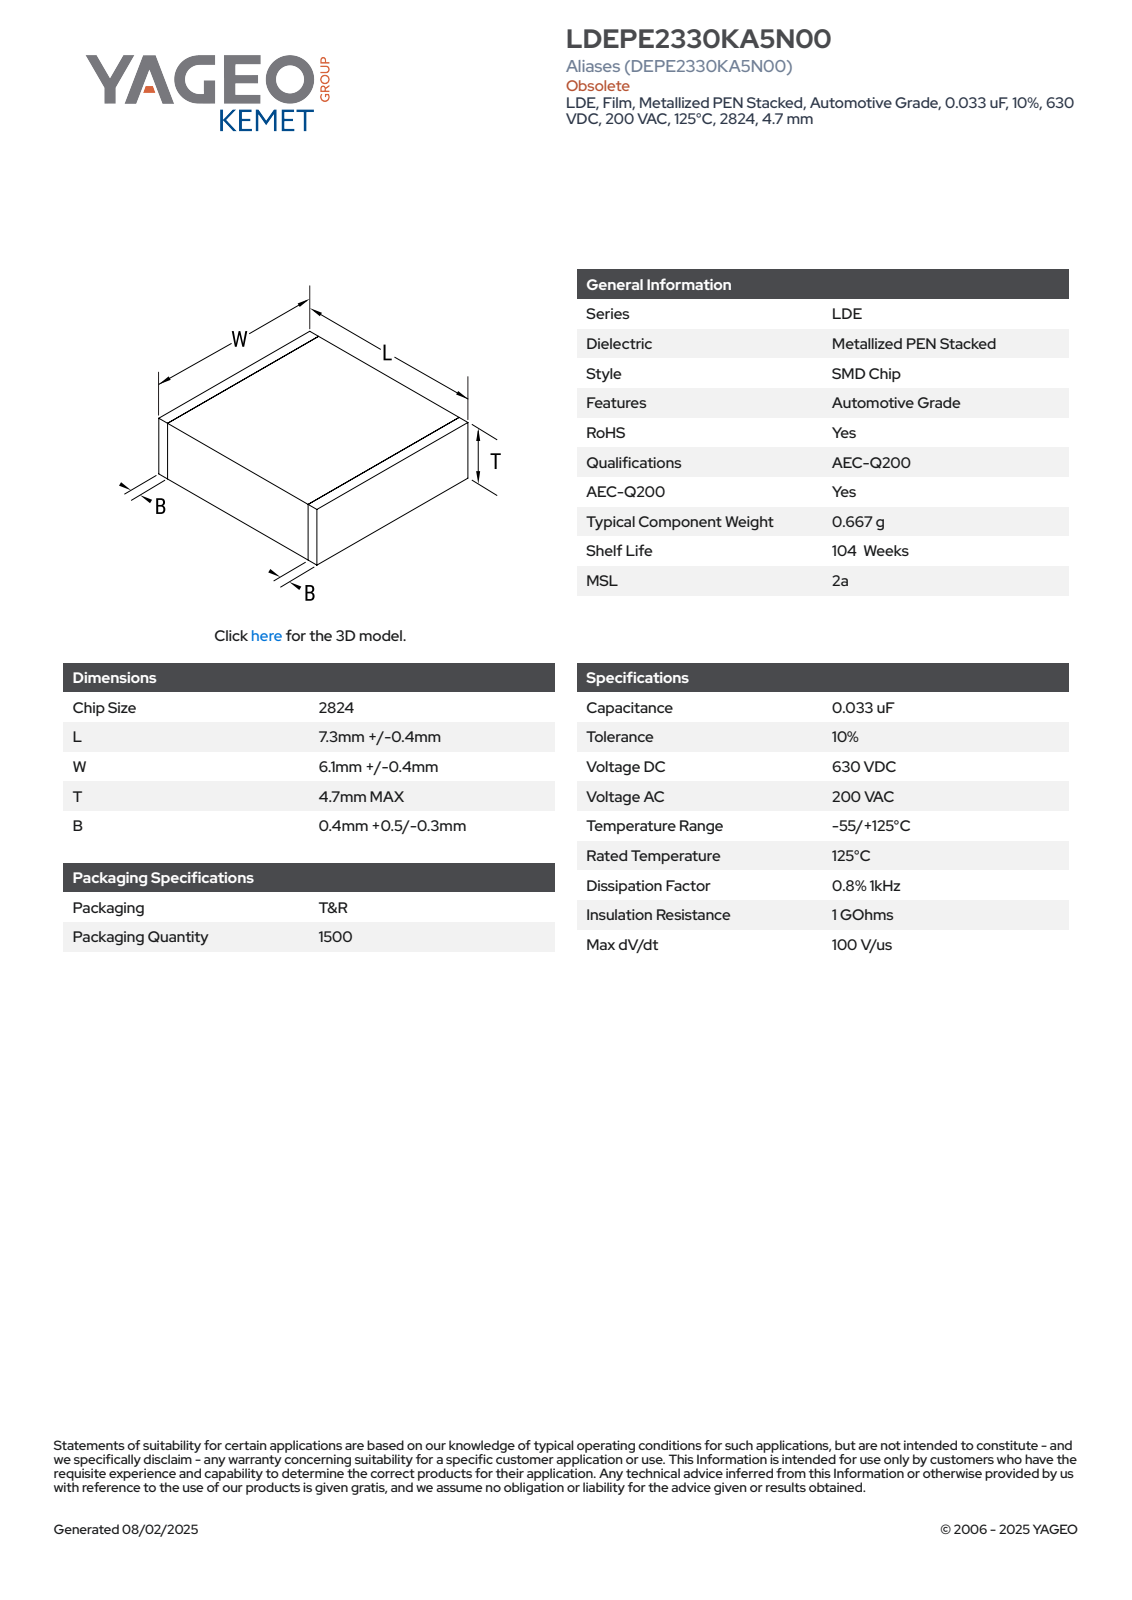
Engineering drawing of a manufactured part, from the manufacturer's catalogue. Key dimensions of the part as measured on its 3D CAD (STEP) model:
Part name (STEP PRODUCT): CFS_LDELDB_2824_L7.7W6.5T4.7B0.9
STEP written by: SolidWorks 2020 (AUTOMOTIVE_DESIGN)
Units: millimetres
Bodies: 4 solids, 73 faces (73 planar, 0 cylindrical, 0 other)
Overall size (bounding box): 7.7 × 6.5 × 4.7
Volume: 234 mm³ · Surface area: 236 mm²
Main face-to-face distances: 4.68, 6.48, 7.7, 4.69, 6.49, 4.7, 6.5, 0.5, 7.2, 6.7
